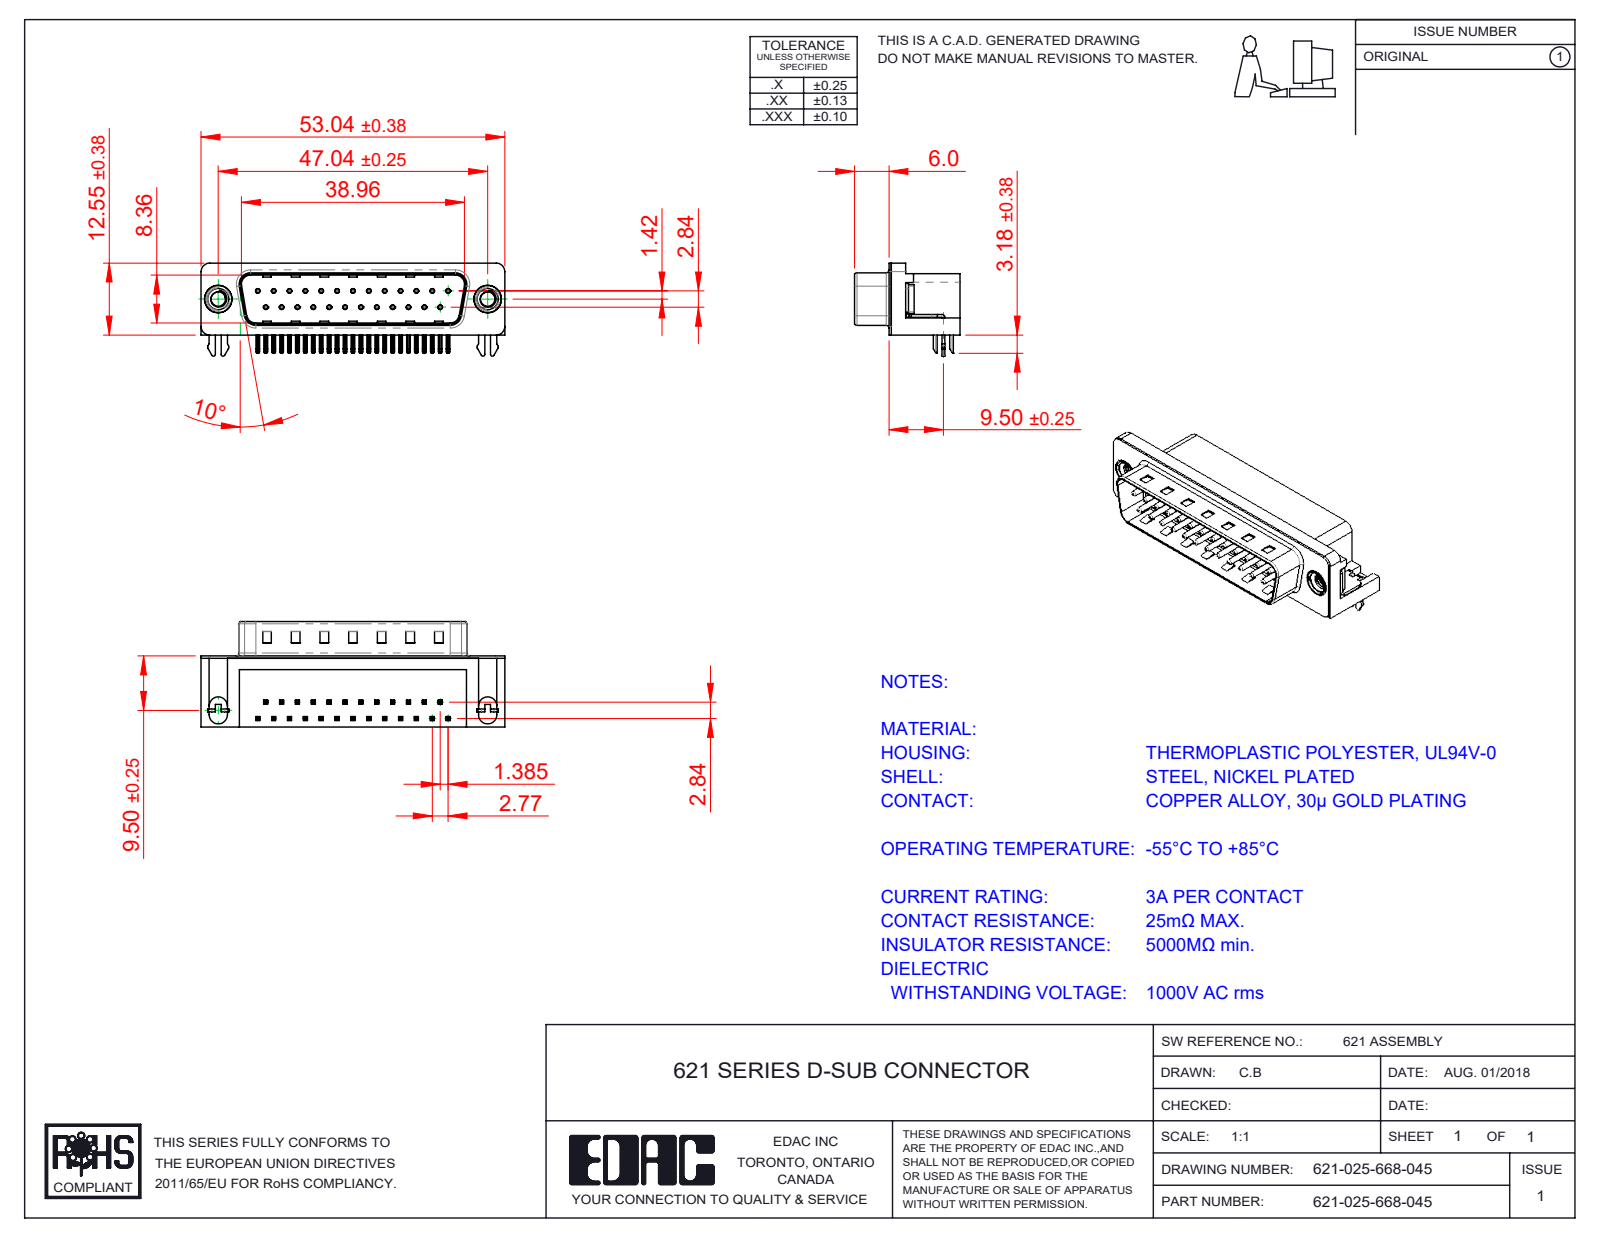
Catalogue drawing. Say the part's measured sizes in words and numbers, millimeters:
The part is named "621 4 Prong Board Lock; 621-025-668-045; 621 Shell_25 Socket; 621 Contact Top (+3 more)". Its 3-D file was written by "SolidWorks 2016 (CONFIG_CONTROL_DESIGN)". It is 31 solids with 2383 faces: 1447 planar, 669 cylindrical and 267 other. Overall it measures 53.04 by 18.4 by 16.25 millimeters. Its volume is 6 352 cubic millimeters and its surface area 7 761 square millimeters. Round holes: 25 of diameter 0.35, 25 of diameter 0.8, 2 of diameter 2, 2 of diameter 2.5, 2 of diameter 4, 2 of diameter 4.8, 2 of diameter 5. Round bosses or shafts: 25 of diameter 0.75, 2 of diameter 4.9, 2 of diameter 4.75, 2 of diameter 3.9, 2 of diameter 3. Partial cylindrical surfaces (rounded edges, fillets, slot ends): 112 of radius 0.25, 50 of radius 0.12, 16 of radius 1, 9 of radius 0.5, 8 of radius 1.6, 7 of radius 1.5, 4 of radius 0.9, 4 of radius 2. The main face-to-face distances are 0.4, 12, 10.35, 2.1, 8.76, 10.46, 1.7, 10.86, 12.4, 9. The hole center spacings are 3.16, 2.77, 5.54, 8.31, 11.08, 13.85, 16.62, 5.03.
